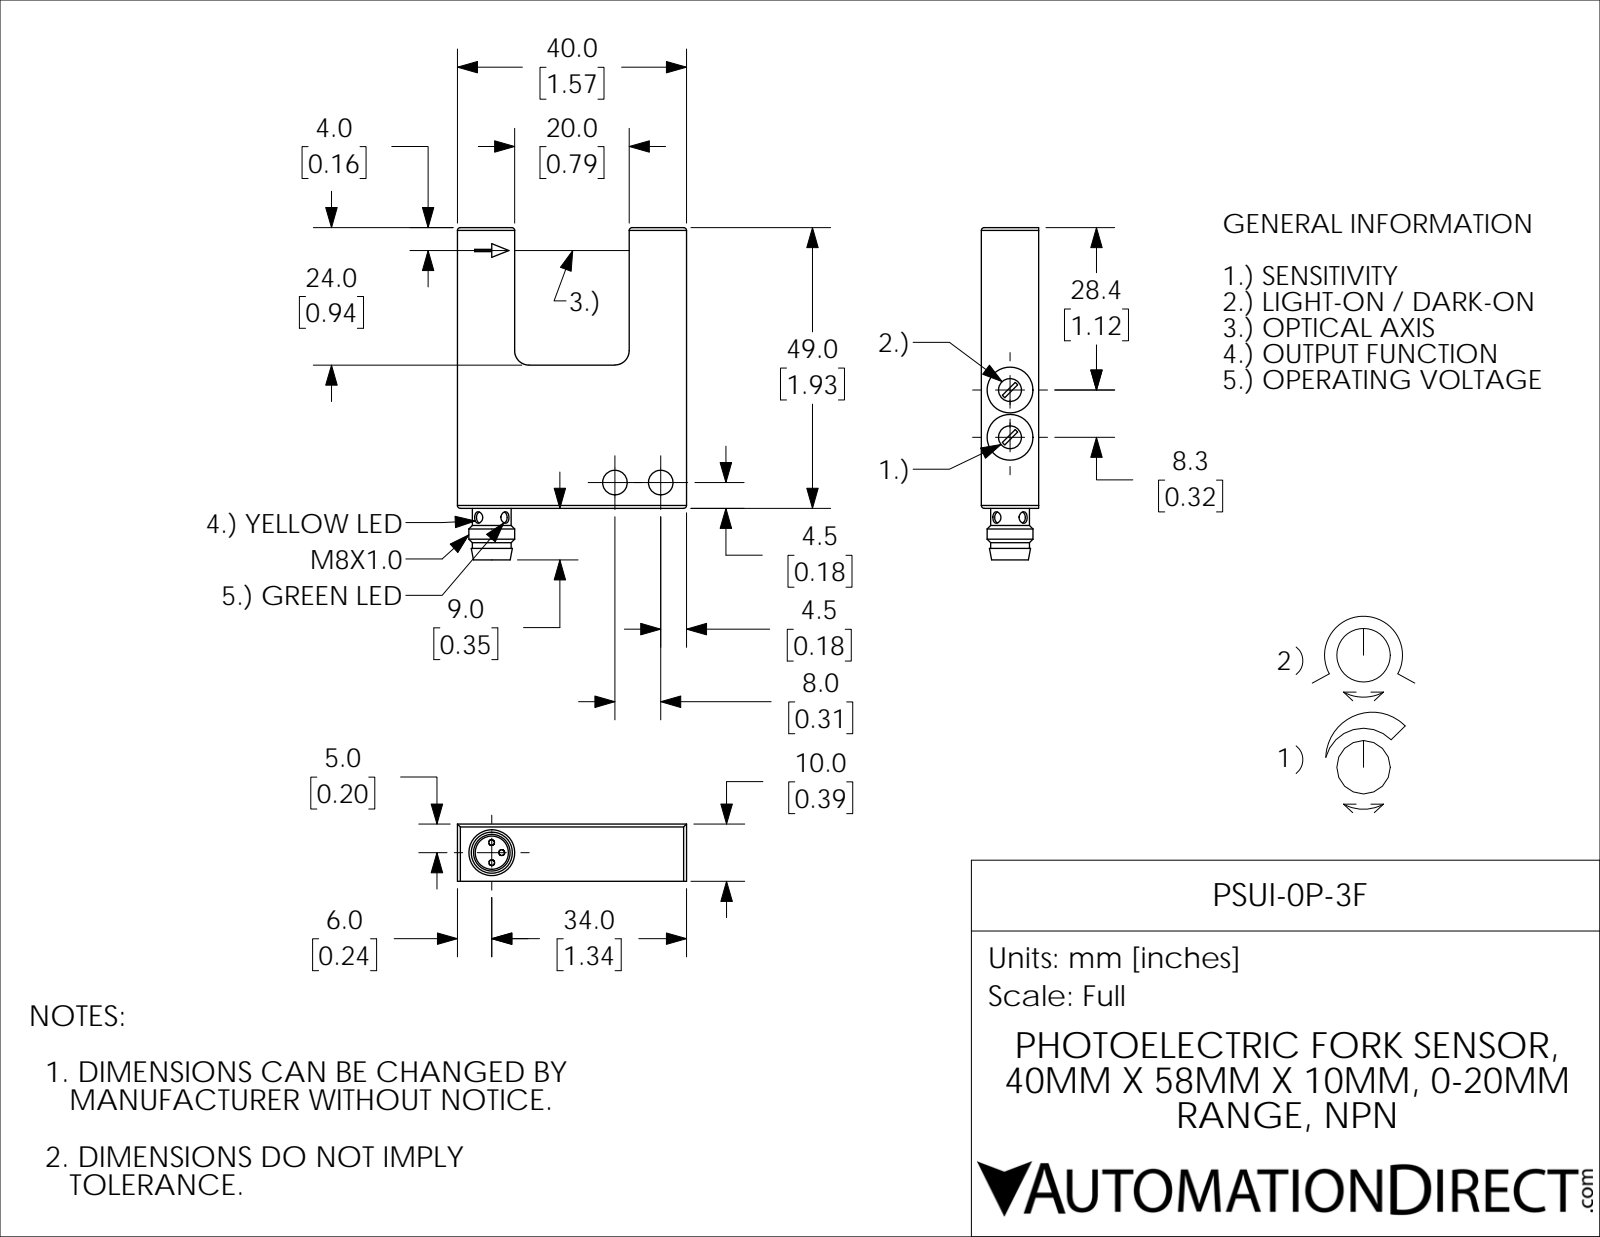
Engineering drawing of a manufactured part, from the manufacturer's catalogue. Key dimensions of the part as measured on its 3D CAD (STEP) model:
Part name (STEP PRODUCT): PSUI-0P-3F
STEP written by: SolidWorks 2017 (AUTOMOTIVE_DESIGN)
Units: inches
Bodies: 1 solid, 73 faces (35 planar, 32 cylindrical, 6 other)
Overall size (bounding box): 2.283 × 1.575 × 0.394
Volume: 0.9 in³ · Surface area: 8.934 in²
Round holes (diameter × count): ⌀0.079 ×2, ⌀0.157 ×2, ⌀0.169 ×2, ⌀0.315 ×2, ⌀0.228 ×1
Round bosses / shafts (diameter × count): ⌀0.039 ×3, ⌀0.315 ×1, ⌀0.267 ×1
Partial cylindrical surfaces — rounded edges, fillets, slot ends (radius × count): R0.02 ×8, R0.063 ×2, R0.098 ×2
Main face-to-face distances: 0.394, 1.181, 1.575, 0.787, 1.929, 0.945, 0.984, 0.39, 1.571, 1.177
Hole centre spacings: 0.315, 0.325
